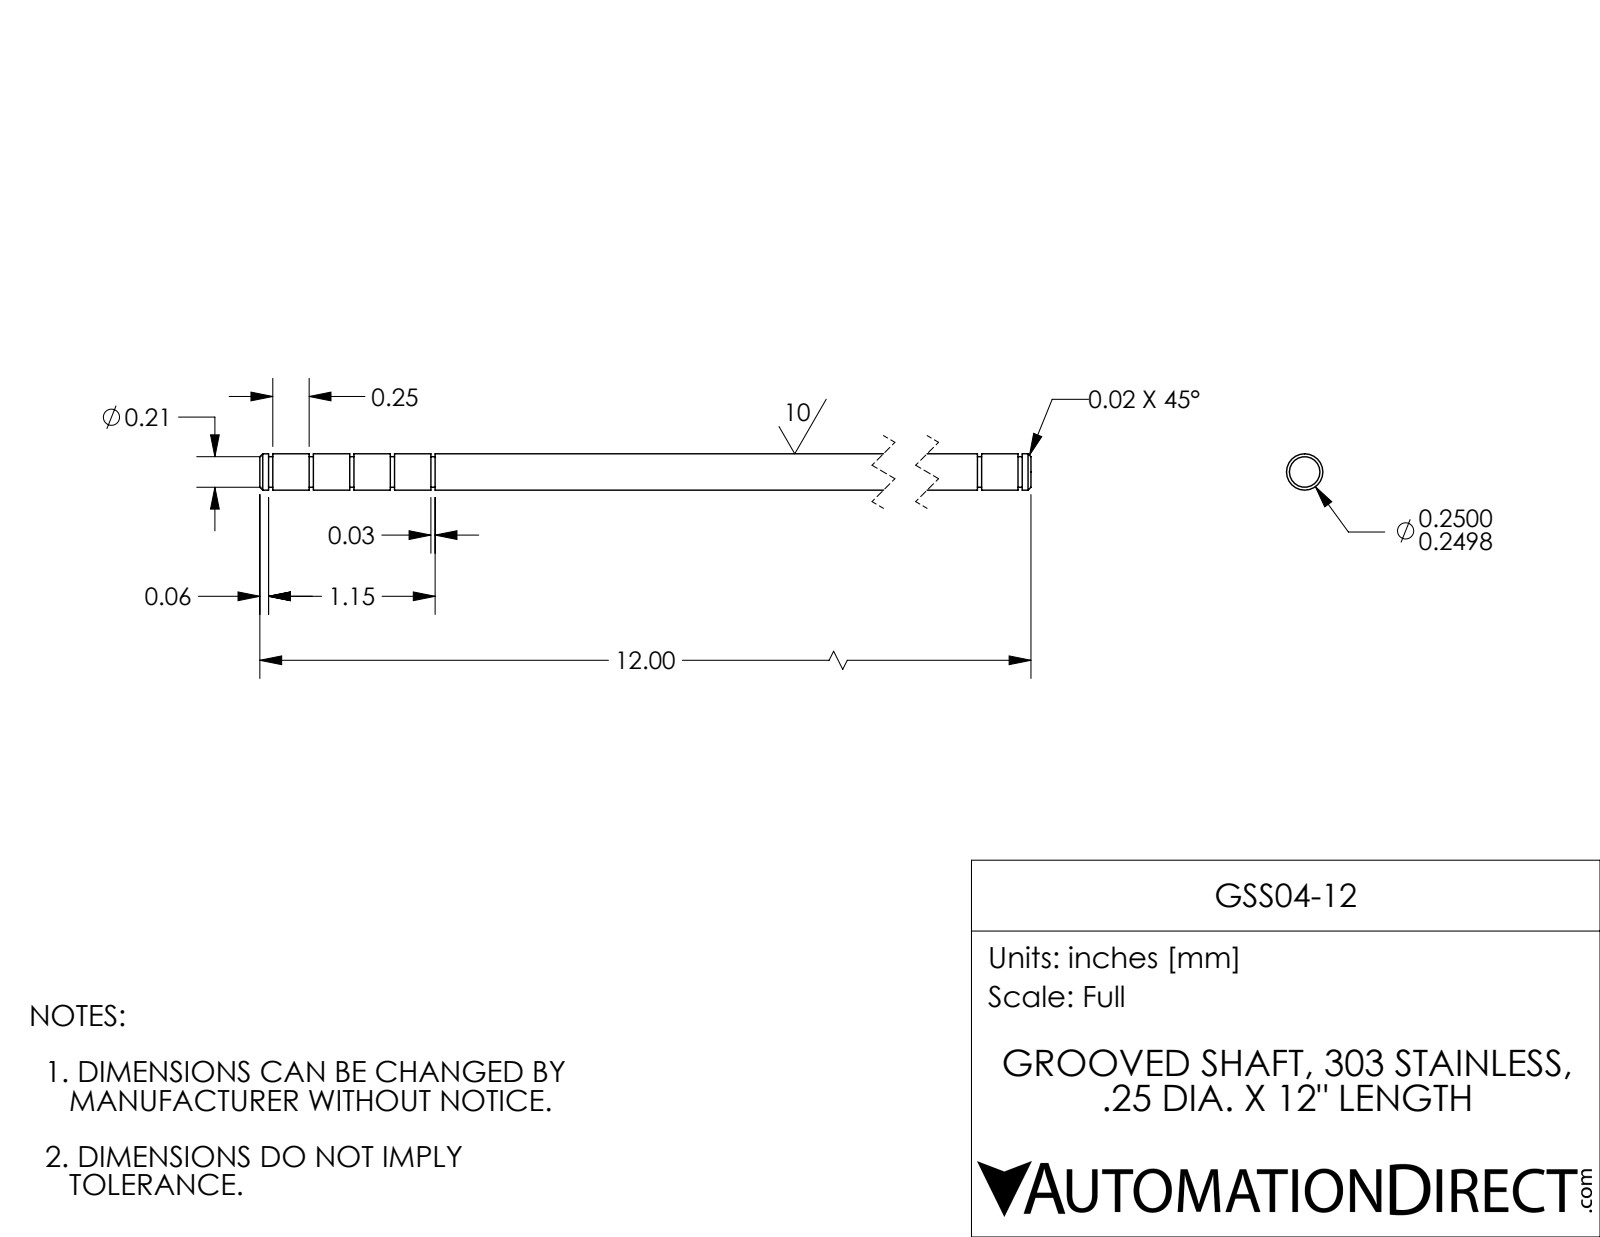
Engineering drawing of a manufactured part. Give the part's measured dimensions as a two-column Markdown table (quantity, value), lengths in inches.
| quantity | value |
| --- | --- |
| part name | GSS04-12 |
| STEP written by | SolidWorks 2017 (AUTOMOTIVE_DESIGN) |
| units | inches |
| bodies | 1 solid, 50 faces (16 planar, 30 cylindrical, 4 other) |
| overall size | 12 × 0.25 × 0.25 |
| volume | 0.586 in³ |
| surface area | 9.68 in² |
| round bosses / shafts (diameter × count) | 0.25 × 1, 0.21 × 1 |
| main face-to-face distances | 0.279, 0.029, 0.25, 0.837, 11.572, 0.558, 10.735, 11.293, 11.014, 0.308 |
